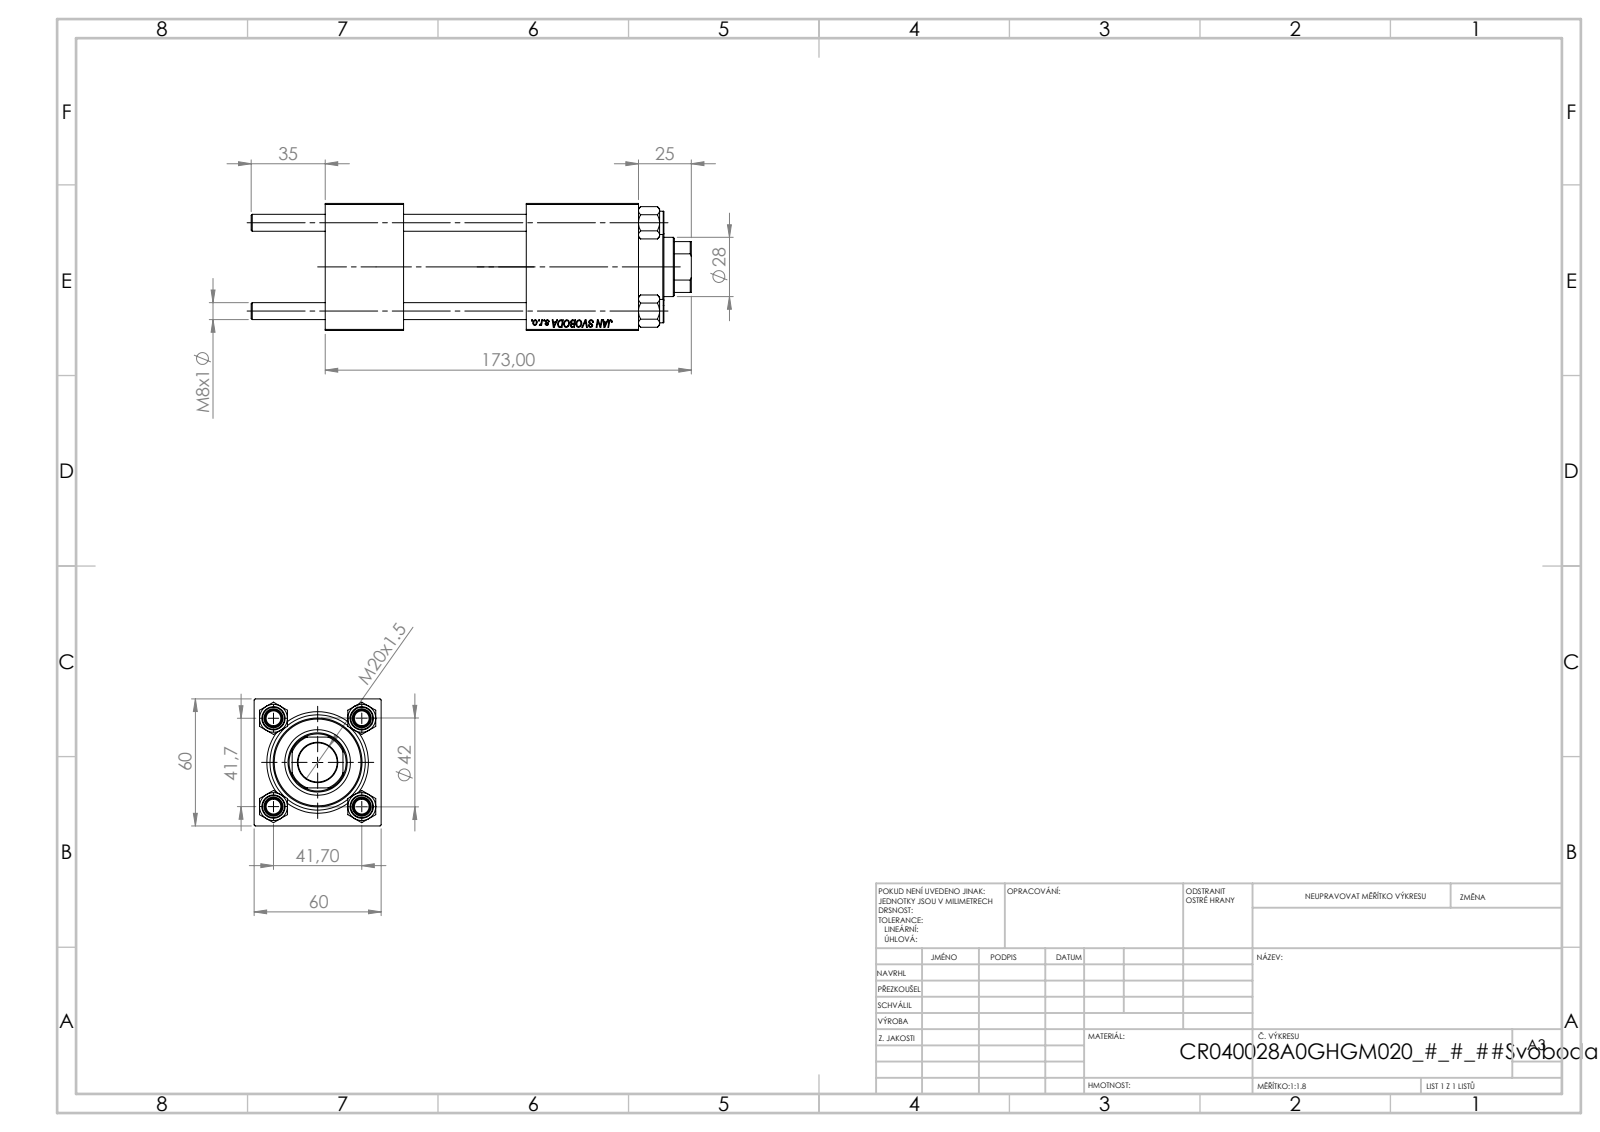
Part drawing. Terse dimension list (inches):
name: V215_VC_A; V215CR_BODY_A; NUT_M5; CR025_012_A_0_G_A_G_M_020_+#_##_TYCINKA (+1 more)
written by: SolidWorks 2019 (CONFIG_CONTROL_DESIGN)
unit: in
bodies: 11 solids, 1135 faces (521 planar, 78 cylindrical, 536 other)
size: 8.189 × 2.362 × 2.362
volume: 26.58 in³; area: 186.2 in²
holes: 4× ⌀0.315, 2× ⌀0.276, 2× ⌀0.656, 2× ⌀0.945, 1× ⌀0.728, 1× ⌀1.102, 1× ⌀1.22, 1× ⌀1.575, 1× ⌀1.772
bosses: 4× ⌀0.433, 1× ⌀1.811, 1× ⌀1.654
rounds: 1× R0.531
face distances: 2.362, 1.457, 2.283, 3.74, 2.087, 5.827, 4.37, 4.697, 3.24, 0.957
hole spacings: 1.161, 1.642, 2.322, 3.642
